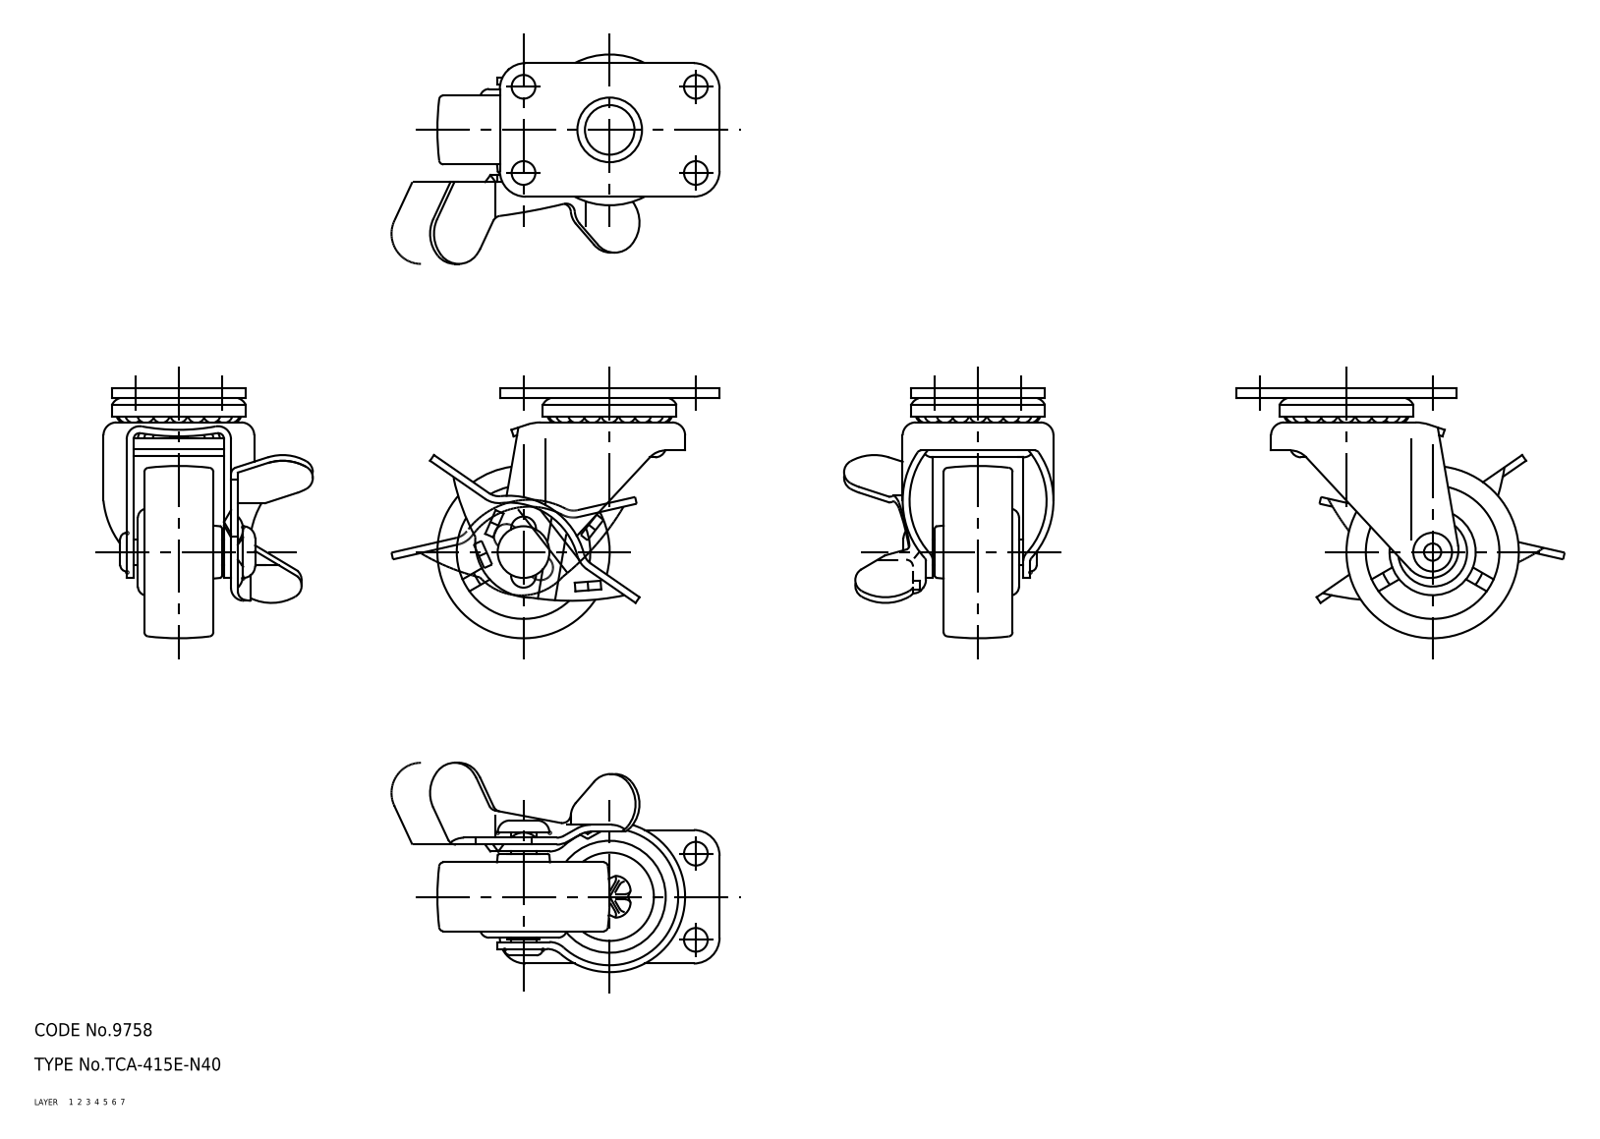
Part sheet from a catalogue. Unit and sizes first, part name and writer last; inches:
Units: inches
Overall size (bounding box): 2.645 × 2.283 × 1.913
Volume: 1.848 in³ · Surface area: 34.47 in²
Bodies: 6 solids, 353 faces (0 planar, 0 cylindrical, 353 other)
Part name (STEP PRODUCT): lever; wheel; mounting plate; main shaft (+2 more)
STEP written by: CADfix (AUTOMOTIVE_DESIGN)
